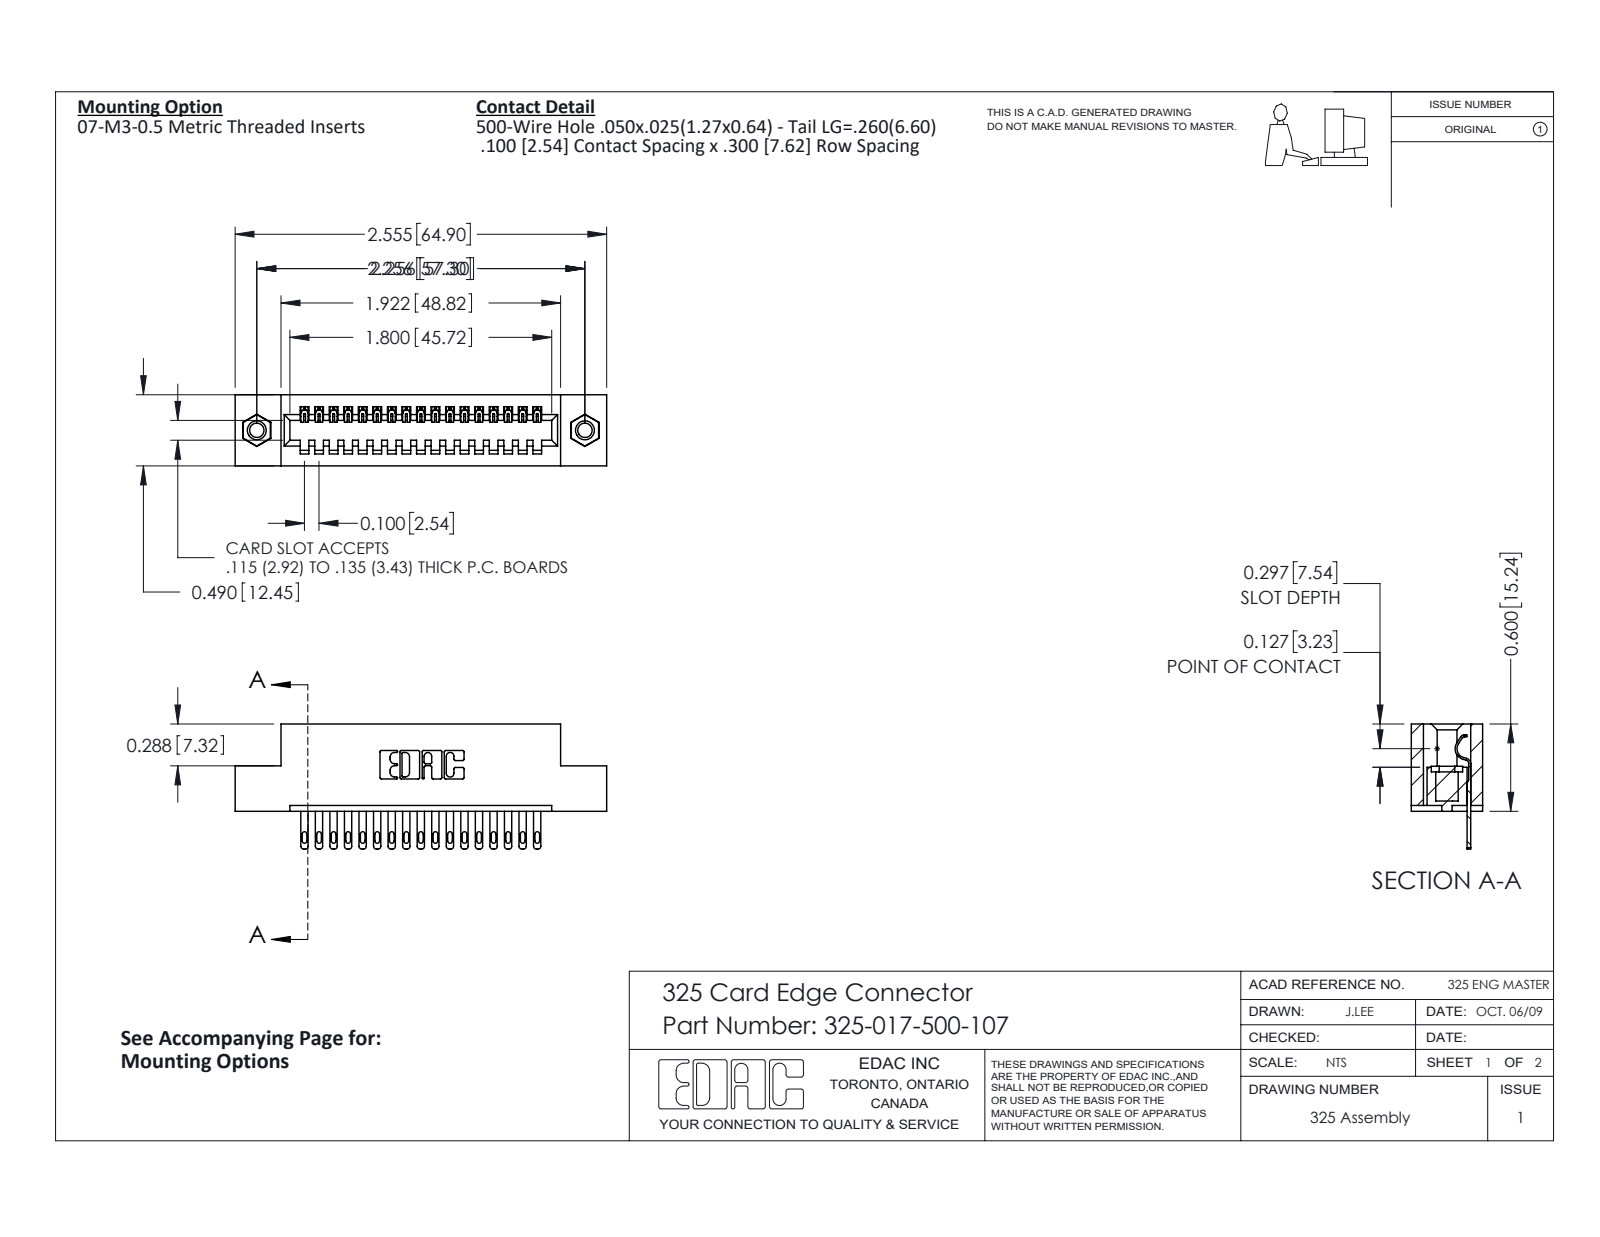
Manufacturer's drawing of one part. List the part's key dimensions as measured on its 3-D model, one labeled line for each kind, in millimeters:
Part name (STEP PRODUCT): 325-292-001_325-293-100; 325-017-500-107; 325 Part_TI; 345-250-001_345-250-005-103
STEP written by: SolidWorks 2016 (CONFIG_CONTROL_DESIGN)
Units: millimetres
Bodies: 20 solids, 1092 faces (714 planar, 362 cylindrical, 16 other)
Overall size (bounding box): 64.9 × 21.8 × 12.4
Volume: 8 050 mm³ · Surface area: 8 426 mm²
Round holes (diameter × count): ⌀2.5 ×2, ⌀3.2 ×2, ⌀4.1 ×2
Round bosses / shafts (diameter × count): ⌀3.9 ×2
Partial cylindrical surfaces — rounded edges, fillets, slot ends (radius × count): R0.2 ×34, R0.4 ×34, R0.5 ×34, R0.3 ×22, R0.2 ×6, R0.8 ×6, R0.7 ×3, R0.4 ×1
Main face-to-face distances: 2.1, 10.3, 7.6, 12.4, 2.7, 9.7, 0.6, 15.2, 1, 5.1
Hole centre spacings: 57.3
